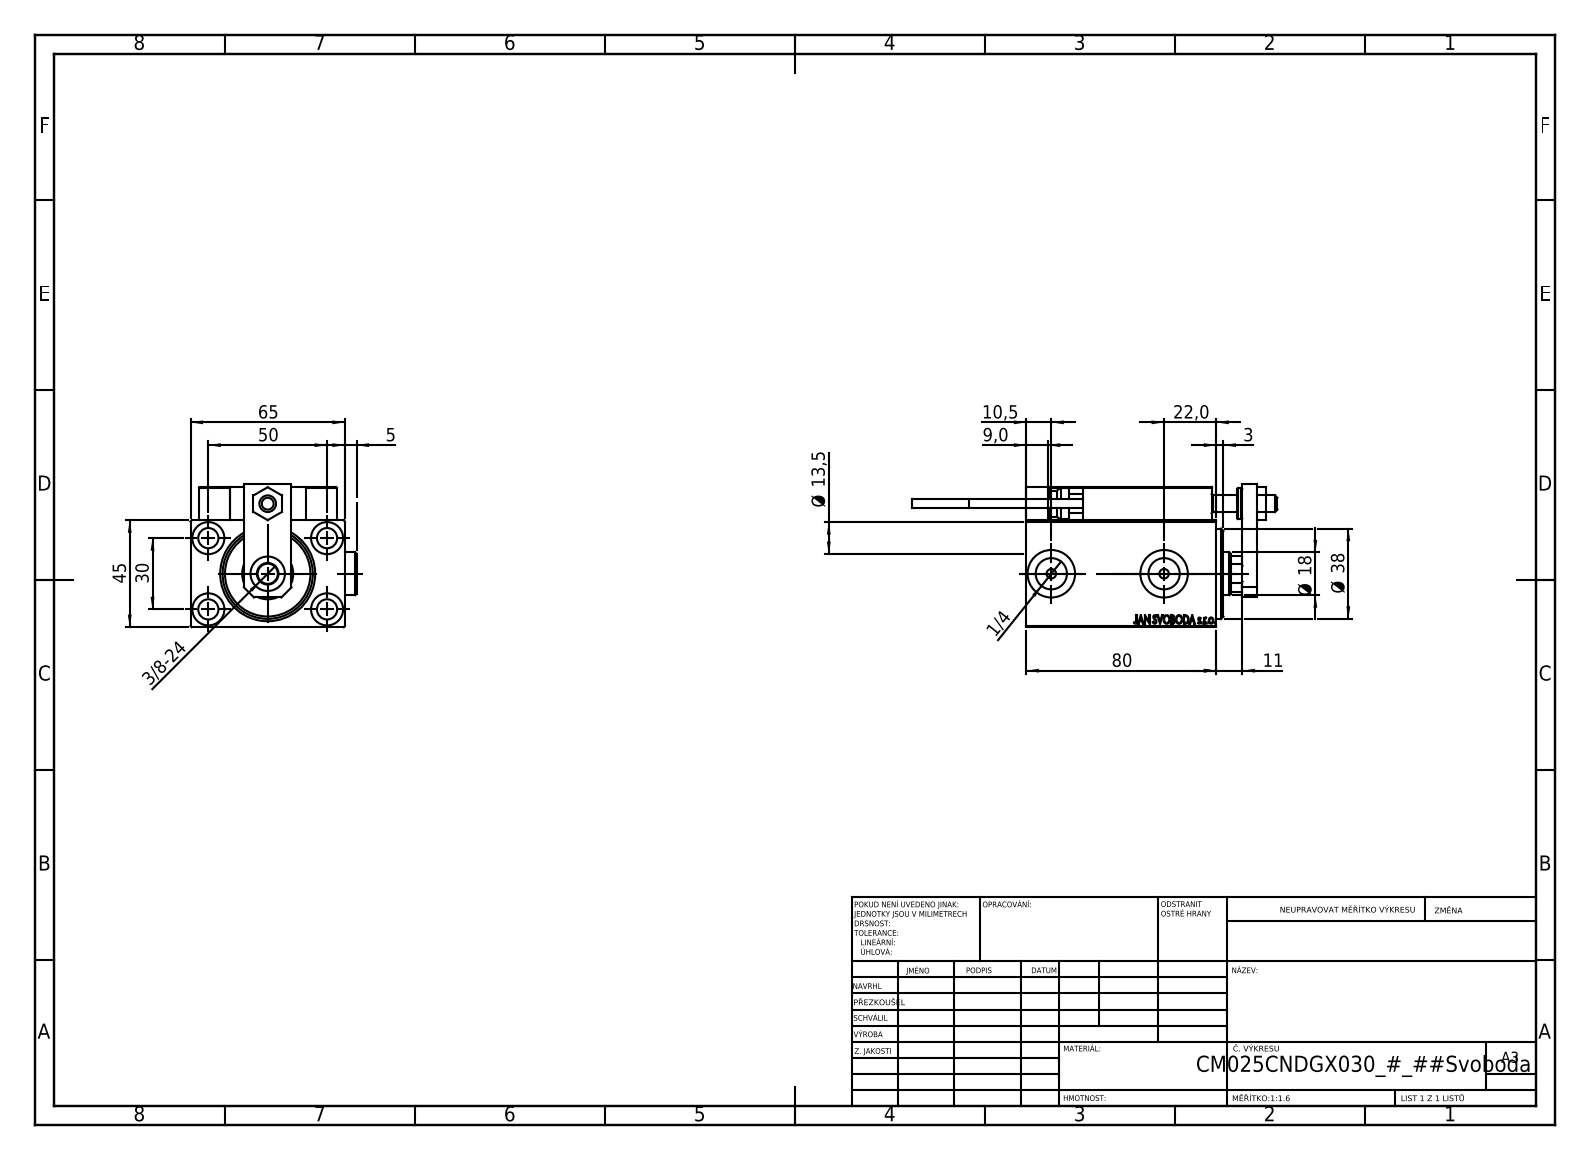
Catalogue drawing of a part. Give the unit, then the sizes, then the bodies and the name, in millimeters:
Units: millimetres
Overall size (bounding box): 153.7 × 69.9 × 60.5
Round holes (diameter × count): ⌀4 ×6, ⌀8 ×5, ⌀8.5 ×5, ⌀3.2 ×4, ⌀13.5 ×4, ⌀5 ×2, ⌀13.16 ×2, ⌀20 ×2, ⌀7 ×1, ⌀14.5 ×1, ⌀18 ×1, ⌀21.5 ×1
Round bosses / shafts (diameter × count): ⌀18 ×2, ⌀5 ×2, ⌀3.8 ×2, ⌀13 ×1, ⌀11 ×1
Partial cylindrical surfaces — rounded edges, fillets, slot ends (radius × count): R0.3 ×30, R3 ×2, R8.5 ×1
Main face-to-face distances: 45, 65, 14, 59, 6, 3, 5, 13, 3.5, 7
Hole centre spacings: 29.15, 11.37, 20, 28.9, 29.59, 29.69, 30, 32.06
Volume: 246 749 mm³ · Surface area: 76 934 mm²
Bodies: 25 solids, 1336 faces (594 planar, 204 cylindrical, 538 other)
Part name (STEP PRODUCT): KONCOVKA; SWITCH DIM B,W; V450CM_C_VCP; NUT_D12 (+8 more)
STEP written by: SolidWorks 2019 (CONFIG_CONTROL_DESIGN)
